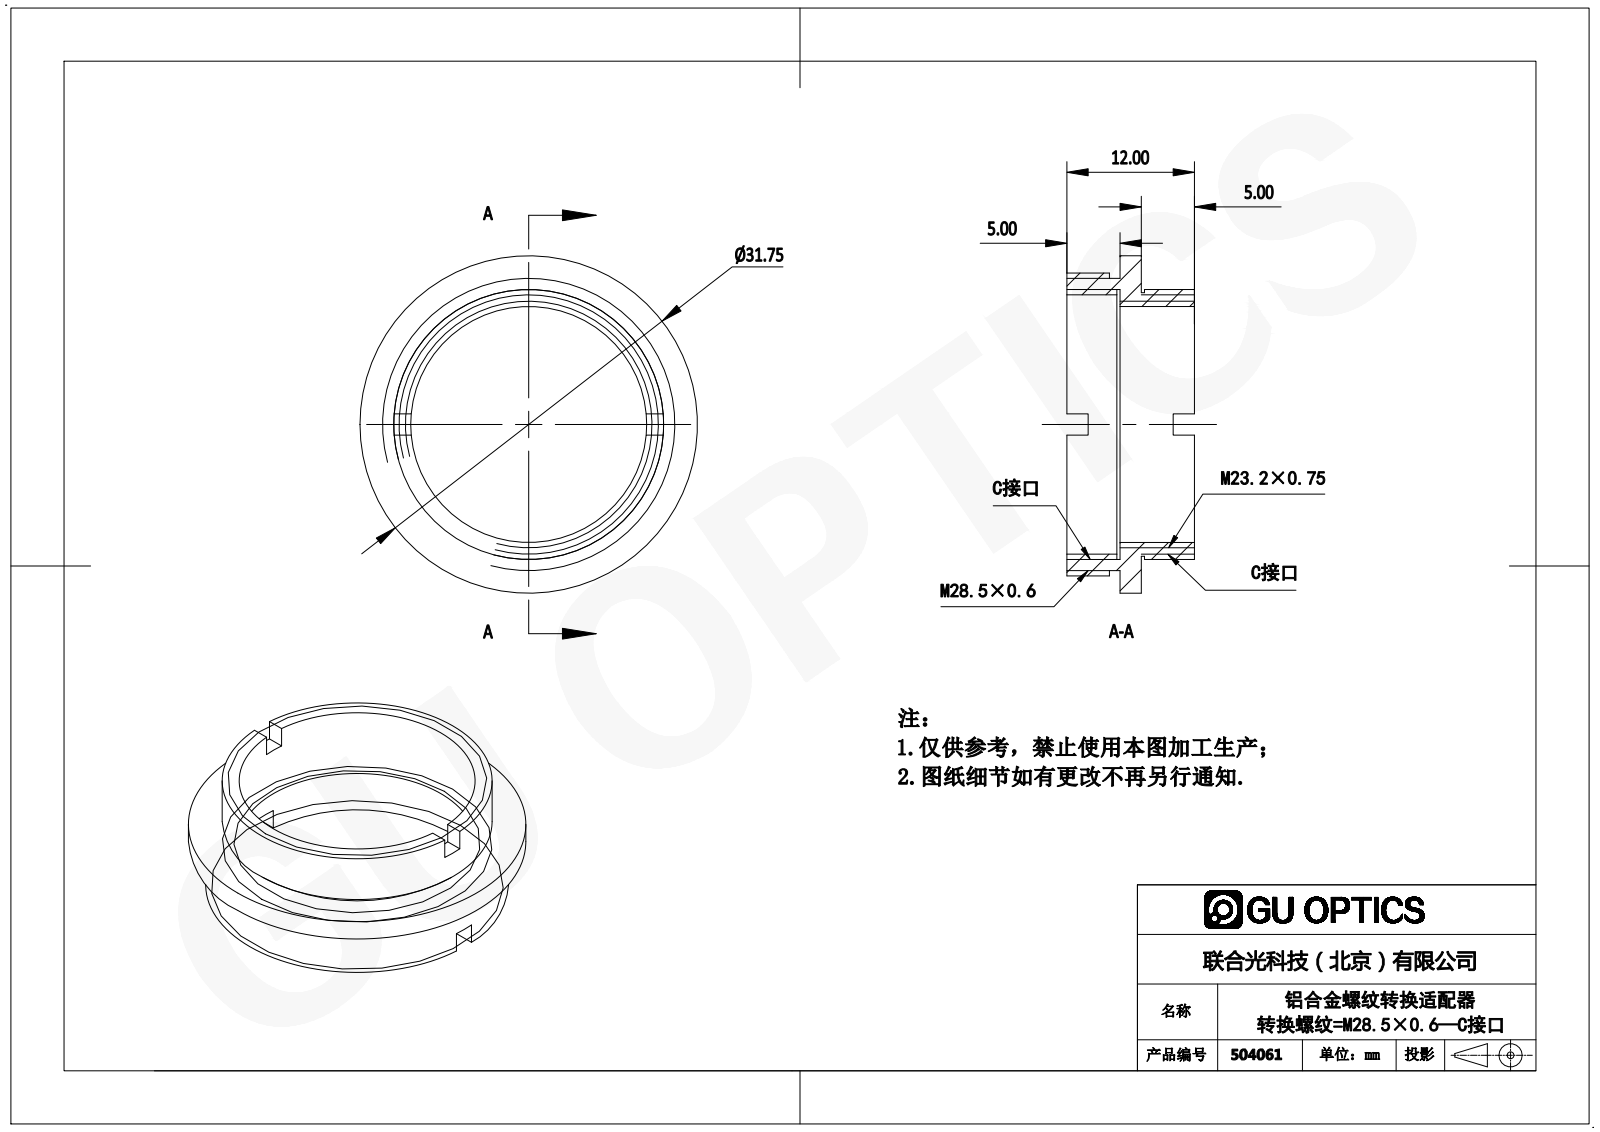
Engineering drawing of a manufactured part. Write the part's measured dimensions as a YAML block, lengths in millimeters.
part_name: "504061"
step_written_by: "SolidWorks 2016 (AUTOMOTIVE_DESIGN)"
units: millimeters
bodies: {solids: 1, faces: 38, planar: 22, cylindrical: 16, other: 0}
overall_size: [31.75, 31.75, 12]
volume: 2167
surface_area: 2935
round_holes:
  - {diameter: 22.2, count: 1}
  - {diameter: 24.4, count: 1}
  - {diameter: 25.4, count: 1}
round_bosses_or_shafts:
  - {diameter: 31.75, count: 1}
  - {diameter: 28.5, count: 1}
  - {diameter: 27.5, count: 1}
  - {diameter: 24.8, count: 1}
face_to_face_distances: [2, 5, 7, 12, 4.7, 7.3, 2.3, 3, 8, 4]
